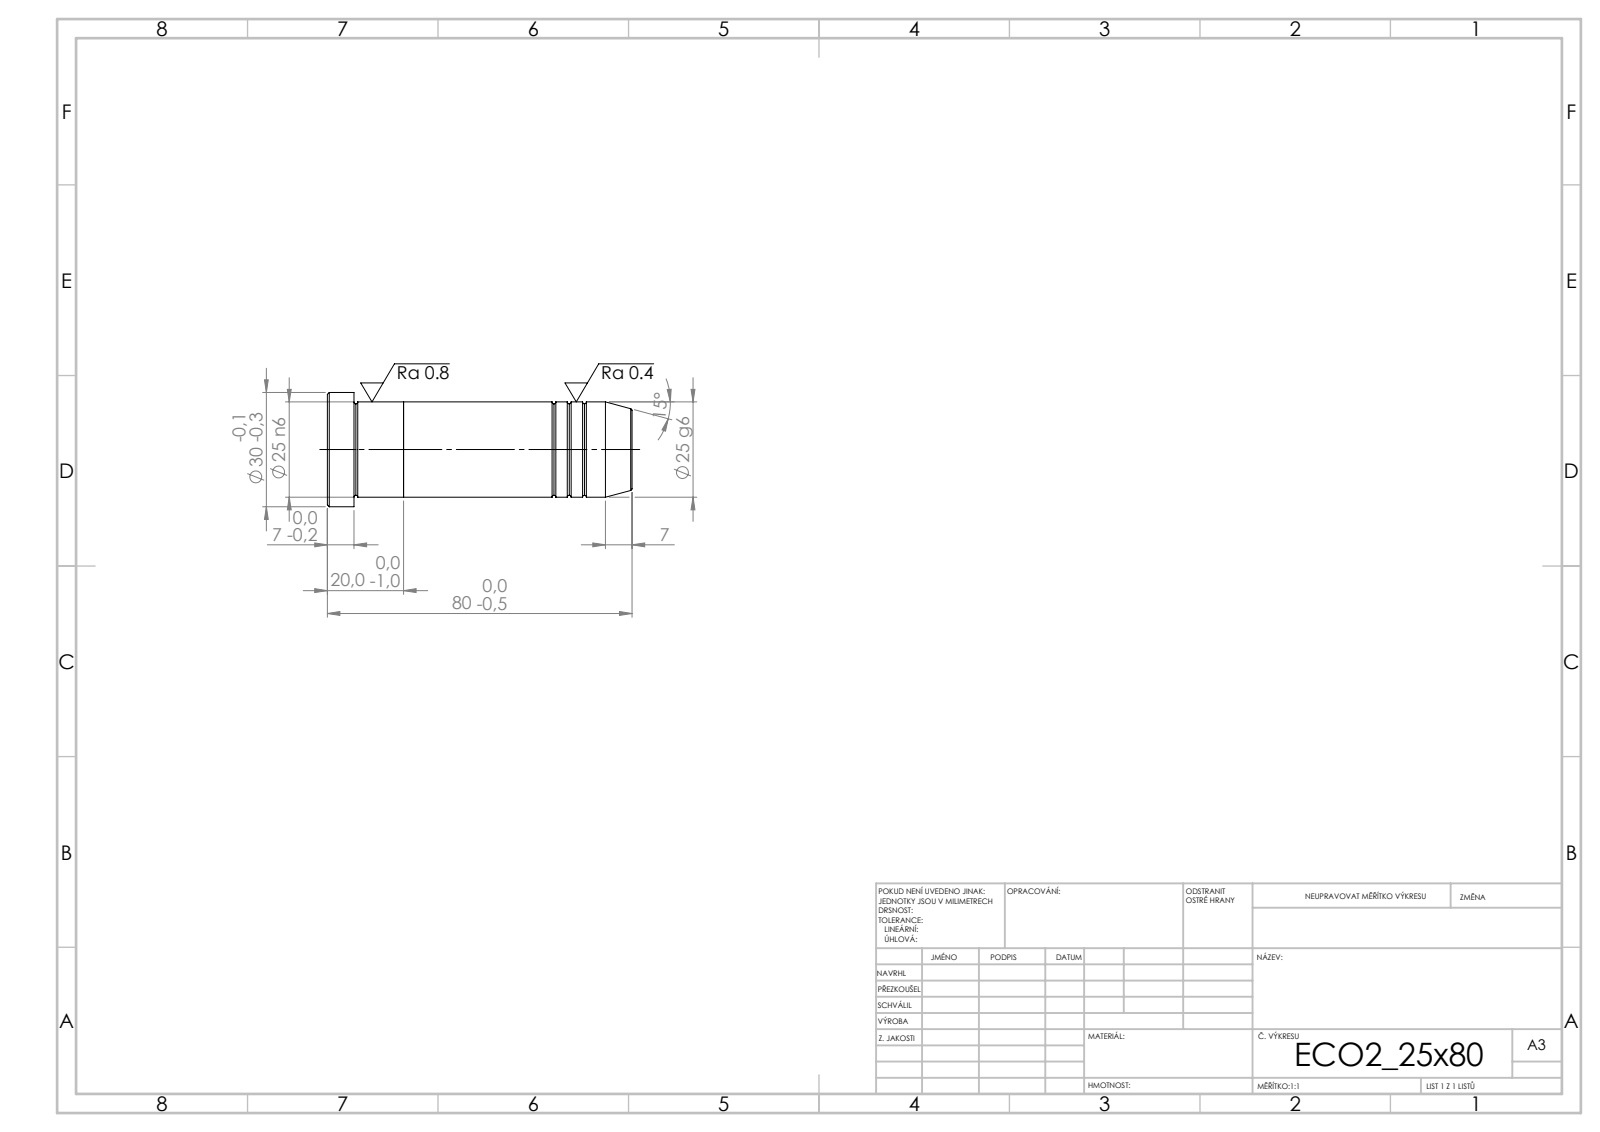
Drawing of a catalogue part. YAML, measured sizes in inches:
step_written_by: "SolidWorks 2019 (CONFIG_CONTROL_DESIGN)"
units: inches
bodies: {solids: 2, faces: 39, planar: 5, cylindrical: 12, other: 22}
overall_size: [3.15, 1.181, 1.181]
volume: 2.451
surface_area: 13.58
round_bosses_or_shafts:
  - {diameter: 1.181, count: 1}
  - {diameter: 0.984, count: 1}
face_to_face_distances: [0.787, 2.362, 3.15, 2.874, 0.512, 0.276]
